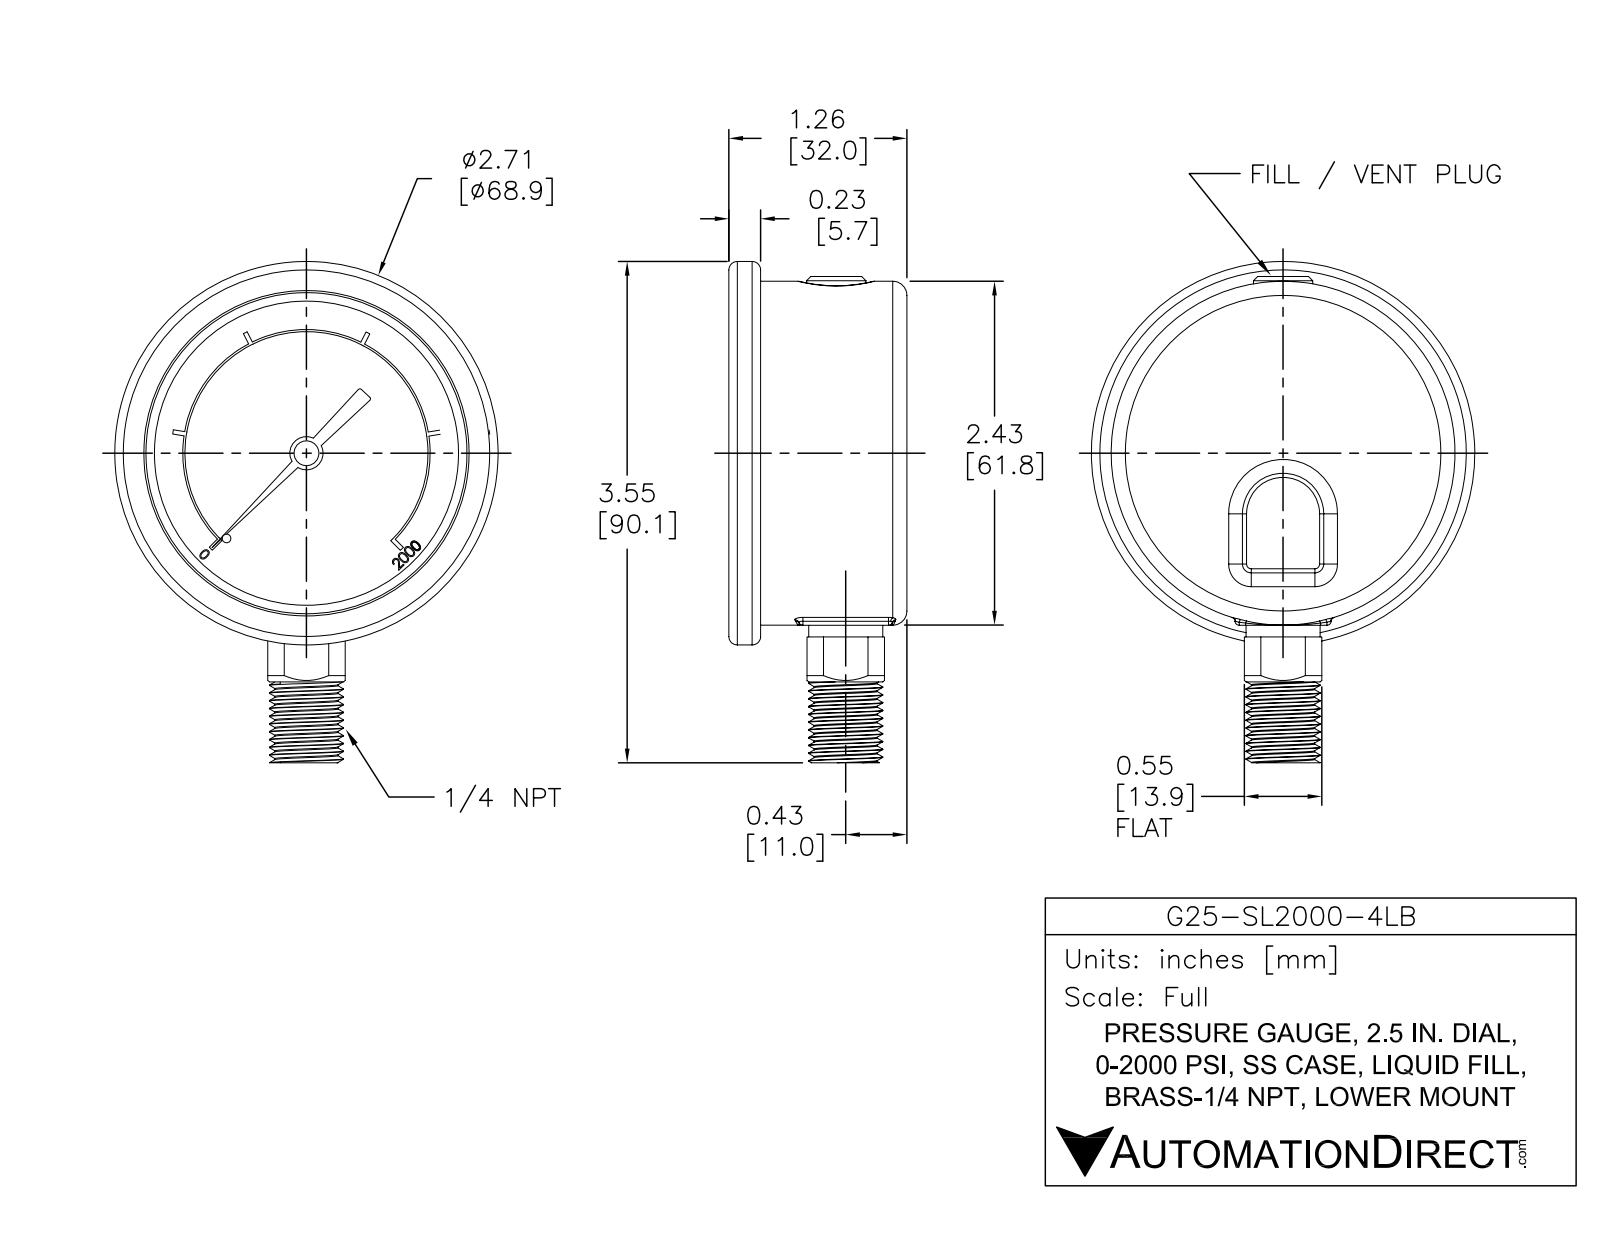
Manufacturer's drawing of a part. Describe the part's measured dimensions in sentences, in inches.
The part is named "G25-SL2000-4LB". Its 3-D file was written by "SolidWorks 2021 (AUTOMOTIVE_DESIGN)". It is 1 solid with 365 faces: 210 planar, 83 cylindrical and 72 other. Overall it measures 2.713 by 2.713 by 2.23 inches. Its volume is 5.168 cubic inches and its surface area 24.83 square inches. Round holes: 1 of diameter 0.071, 1 of diameter 0.098, 1 of diameter 2.272. Round bosses or shafts: 1 of diameter 2.713, 1 of diameter 2.433, 1 of diameter 0.545, 1 of diameter 0.54, 1 of diameter 0.42, 1 of diameter 0.235, 1 of diameter 0.176, 1 of diameter 0.14. Partial cylindrical surfaces (rounded edges, fillets, slot ends): 8 of radius 0.06, 2 of radius 0.015, 1 of radius 0.304, 1 of radius 0.86, 1 of radius 0.875. The main face-to-face distances are 0.95, 1.2, 0.25, 0.06, 1.01, 1.26, 1.035, 0.975, 0.025, 0.225.
